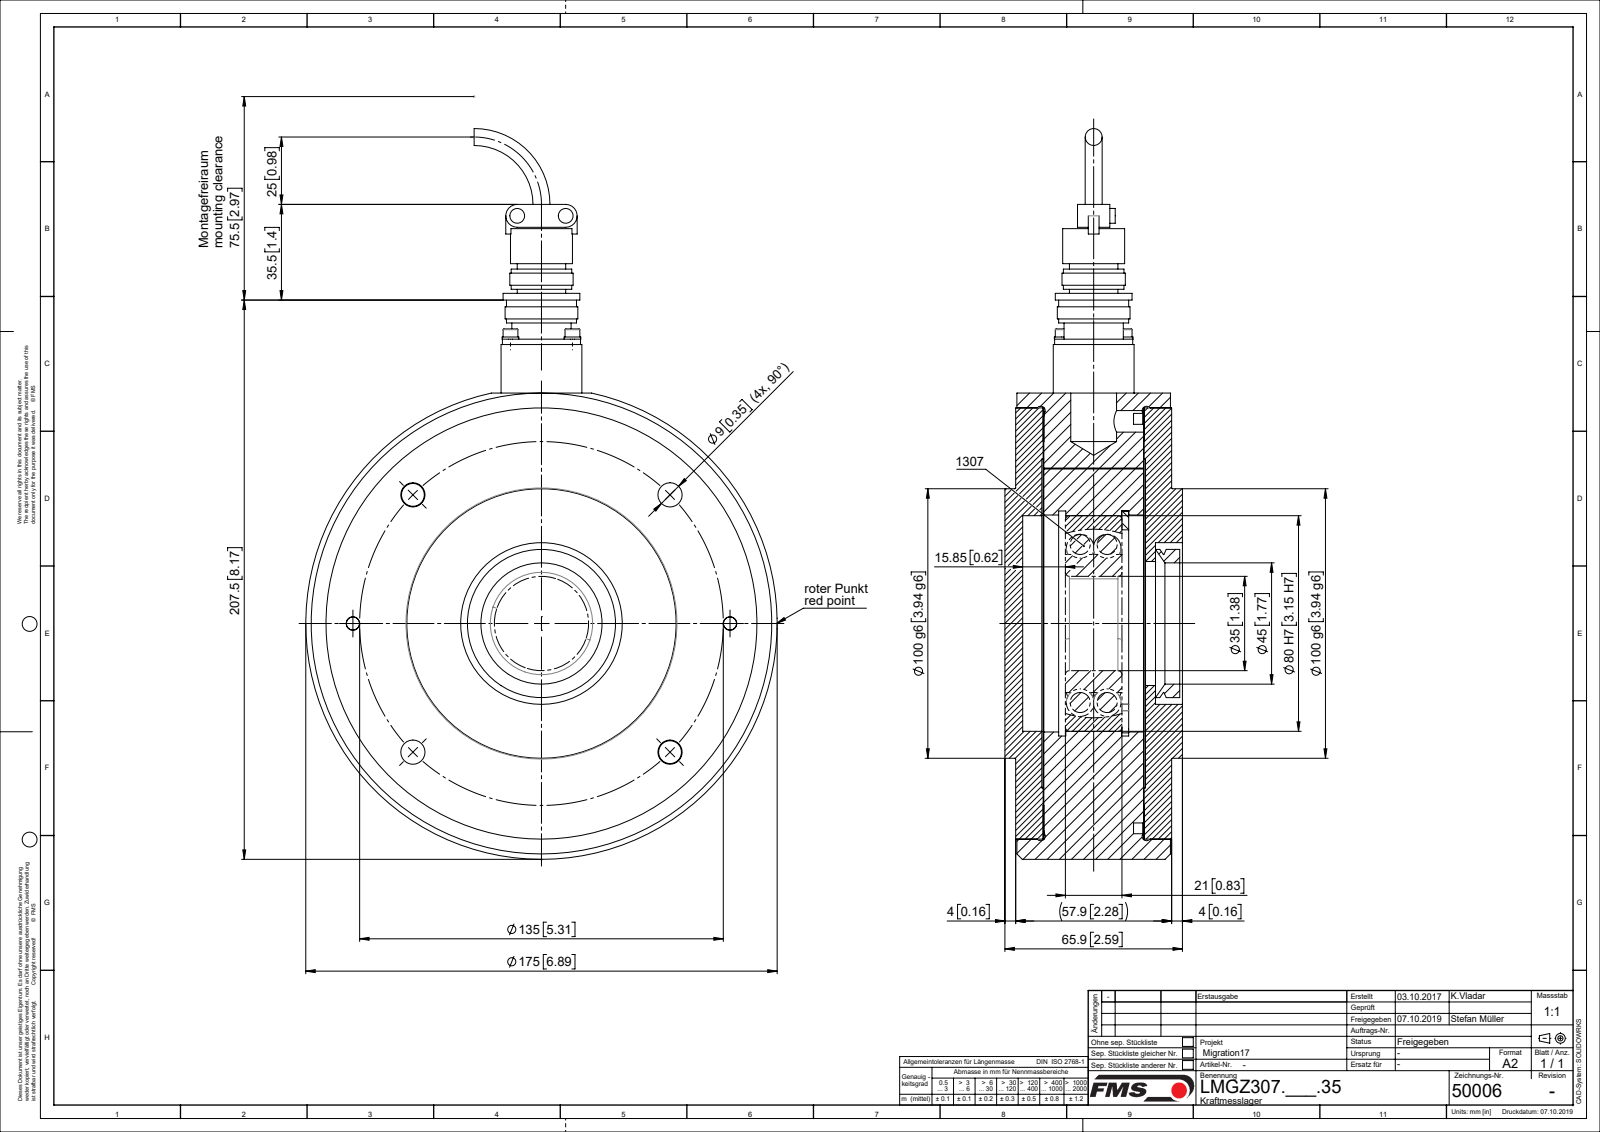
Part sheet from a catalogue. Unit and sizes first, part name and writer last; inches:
Units: inches
Overall size (bounding box): 12.5 × 10.675 × 4.122
Round holes (diameter × count): ⌀0.102 ×4, ⌀0.126 ×4, ⌀0.134 ×4, ⌀0.354 ×4, ⌀0.197 ×2, ⌀0.26 ×2, ⌀0.342 ×2, ⌀0.433 ×2, ⌀0.315 ×1, ⌀0.394 ×1, ⌀0.906 ×1, ⌀1.378 ×1
Round bosses / shafts (diameter × count): ⌀0.217 ×6, ⌀0.244 ×4, ⌀0.118 ×4, ⌀0.098 ×4, ⌀0.394 ×2, ⌀0.236 ×2, ⌀6.89 ×1, ⌀6.299 ×1
Partial cylindrical surfaces — rounded edges, fillets, slot ends (radius × count): R0.167 ×2, R0.295 ×2
Main face-to-face distances: 1.467, 0.402, 0.411, 1.868, 1.878, 1.457, 0.02, 1.496, 0.382, 1.898
Hole centre spacings: 0.64, 0.906, 1.918, 2.074, 2.657, 3.758, 4.549, 5.002
Volume: 78.42 in³ · Surface area: 419.4 in²
Bodies: 22 solids, 395 faces (102 planar, 235 cylindrical, 58 other)
Part name (STEP PRODUCT): L50006; L4857104; TEIL1; L48573 (+8 more)
STEP written by: Mechanical Desktop 2007 (CONFIG_CONTROL_DESIGN)
